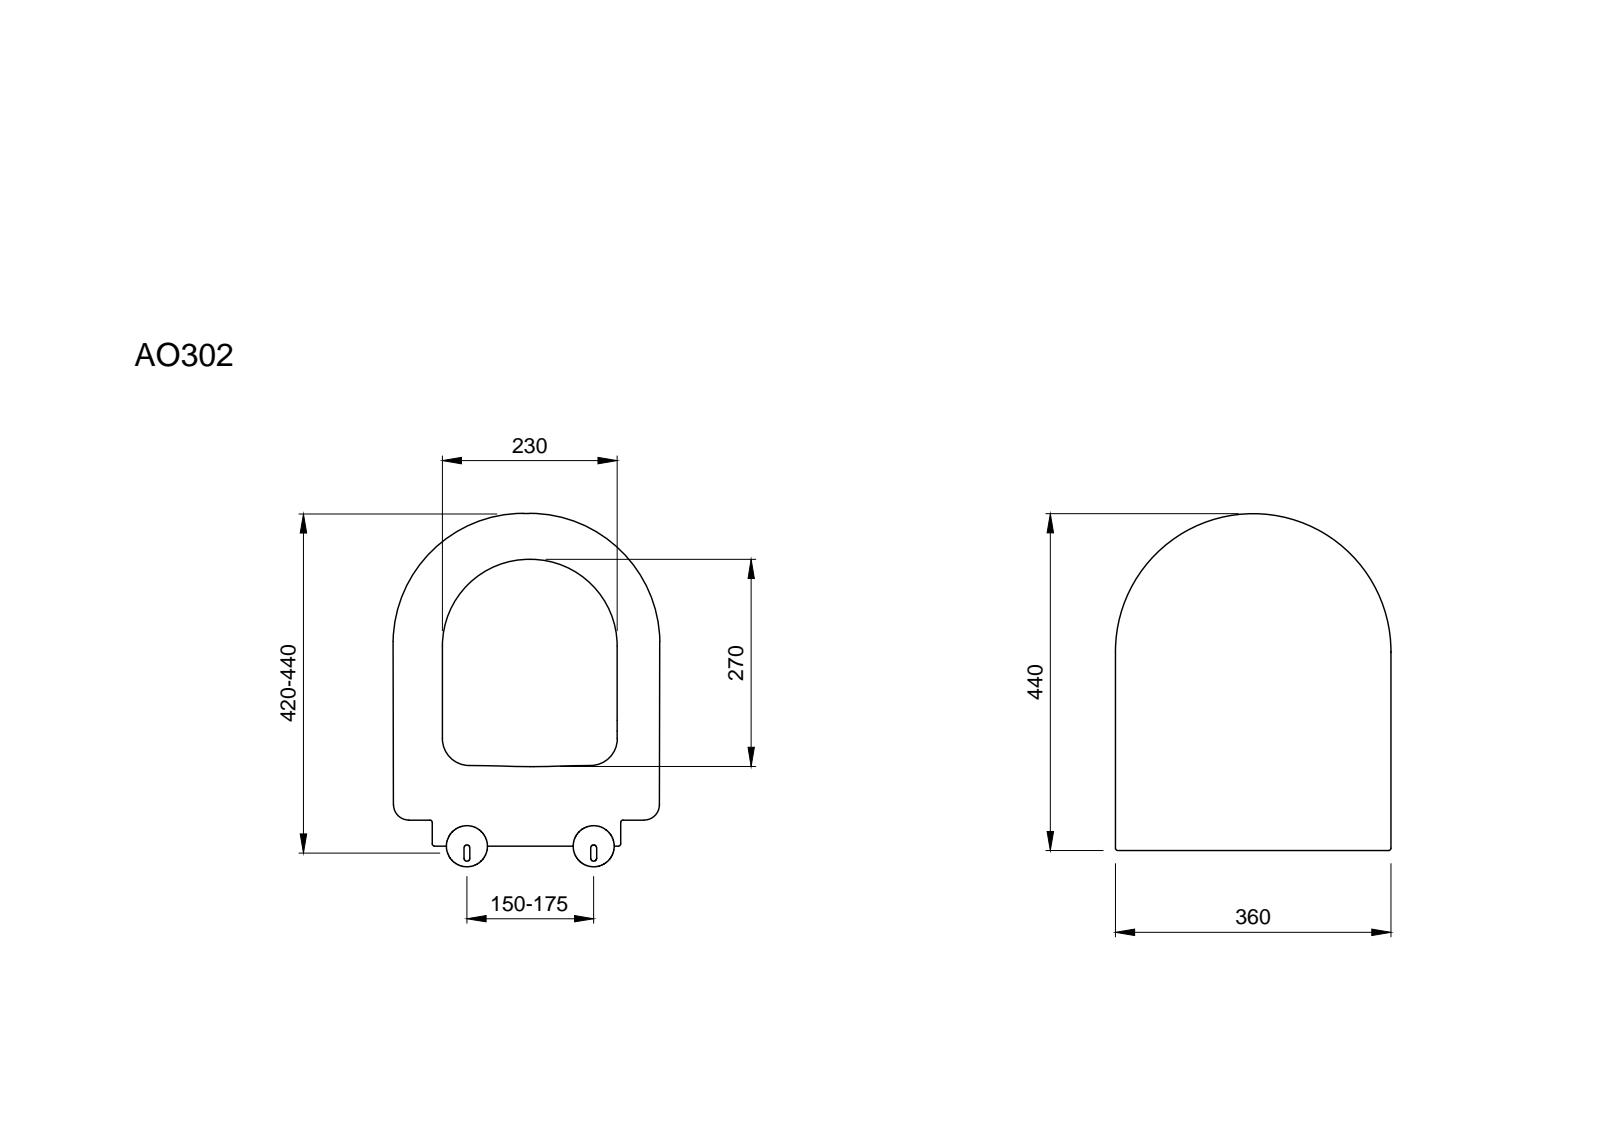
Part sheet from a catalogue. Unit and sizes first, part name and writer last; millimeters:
Units: millimetres
Overall size (bounding box): 428.29 × 360.8 × 54.8
Round bosses / shafts (diameter × count): ⌀12 ×2
Partial cylindrical surfaces — rounded edges, fillets, slot ends (radius × count): R10 ×9, R5 ×8, R15 ×4, R1 ×3, R3 ×2, R8 ×2, R16.5 ×1, R95 ×1
Main face-to-face distances: 5, 15.97, 20.97, 21, 12.99, 32, 37, 142, 137, 121
Volume: 1 594 000 mm³ · Surface area: 594 451 mm²
Bodies: 2 solids, 258 faces (54 planar, 42 cylindrical, 162 other)
Part name (STEP PRODUCT): CAN149894BFg5gc
STEP written by: SIEMENS PLM Software NX 11.0 (AUTOMOTIVE_DESIGN)
